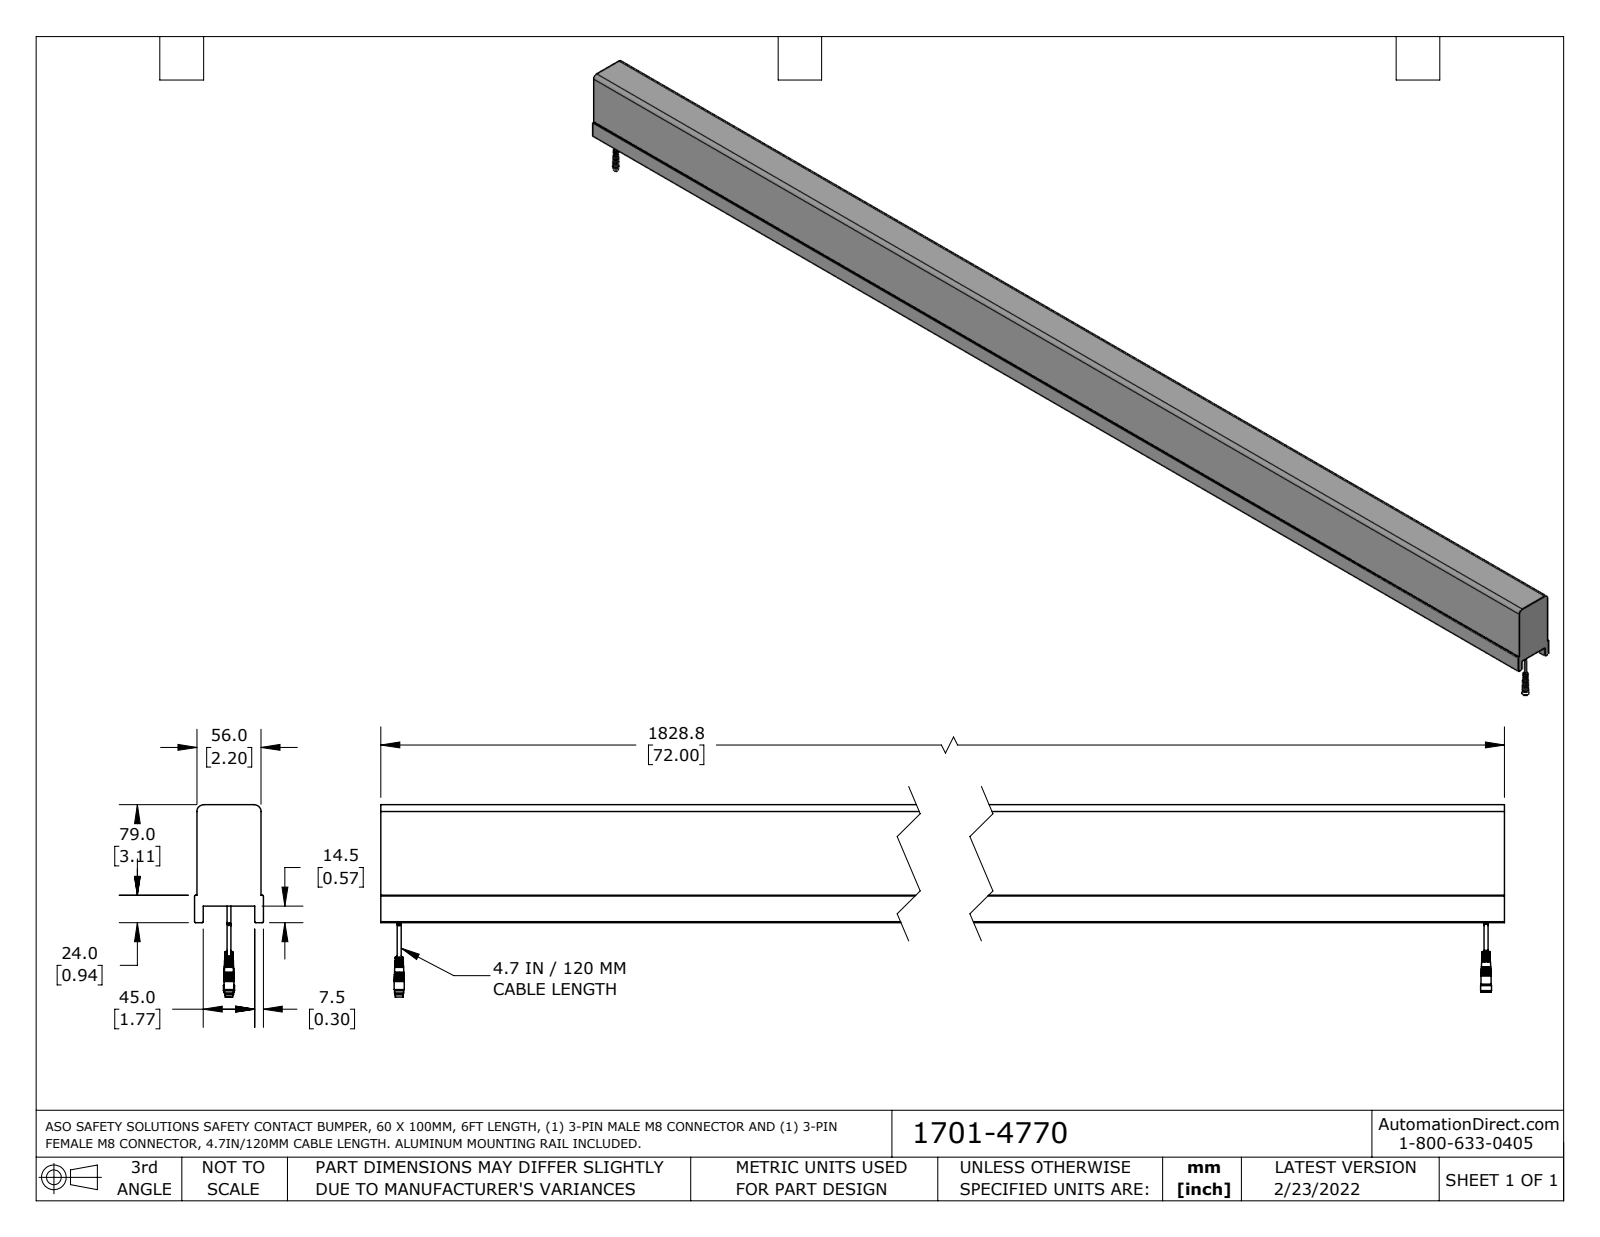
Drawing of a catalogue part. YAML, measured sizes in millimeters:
part_name: "1701-4770_Default"
step_written_by: "SolidWorks 2021 (CONFIG_CONTROL_DESIGN)"
units: millimeters
bodies: {solids: 24, faces: 447, planar: 175, cylindrical: 154, other: 118}
overall_size: [1828.8, 167.9, 60]
volume: 9504000
surface_area: 652900
round_holes:
  - {diameter: 1.2, count: 4}
  - {diameter: 0.8, count: 3}
  - {diameter: 1.6, count: 3}
  - {diameter: 3.4, count: 2}
  - {diameter: 5.8, count: 1}
  - {diameter: 5.9, count: 1}
  - {diameter: 6.9, count: 1}
  - {diameter: 7.2, count: 1}
round_bosses_or_shafts:
  - {diameter: 1.2, count: 8}
  - {diameter: 1, count: 6}
  - {diameter: 0.5, count: 4}
  - {diameter: 8.8, count: 2}
  - {diameter: 5.7, count: 2}
  - {diameter: 3.5, count: 2}
  - {diameter: 9.6, count: 1}
  - {diameter: 9, count: 1}
partial_cylinders:
  - {radius: 1, count: 4}
  - {radius: 0.8, count: 2}
  - {radius: 6, count: 2}
face_to_face_distances: [56, 2, 58, 88.5, 7.5, 52.5, 5.5, 50.5, 60, 45]
hole_center_spacings: [1796.8, 0.7, 1.8, 1798.5, 1, 1.4, 1.9, 2.4]
